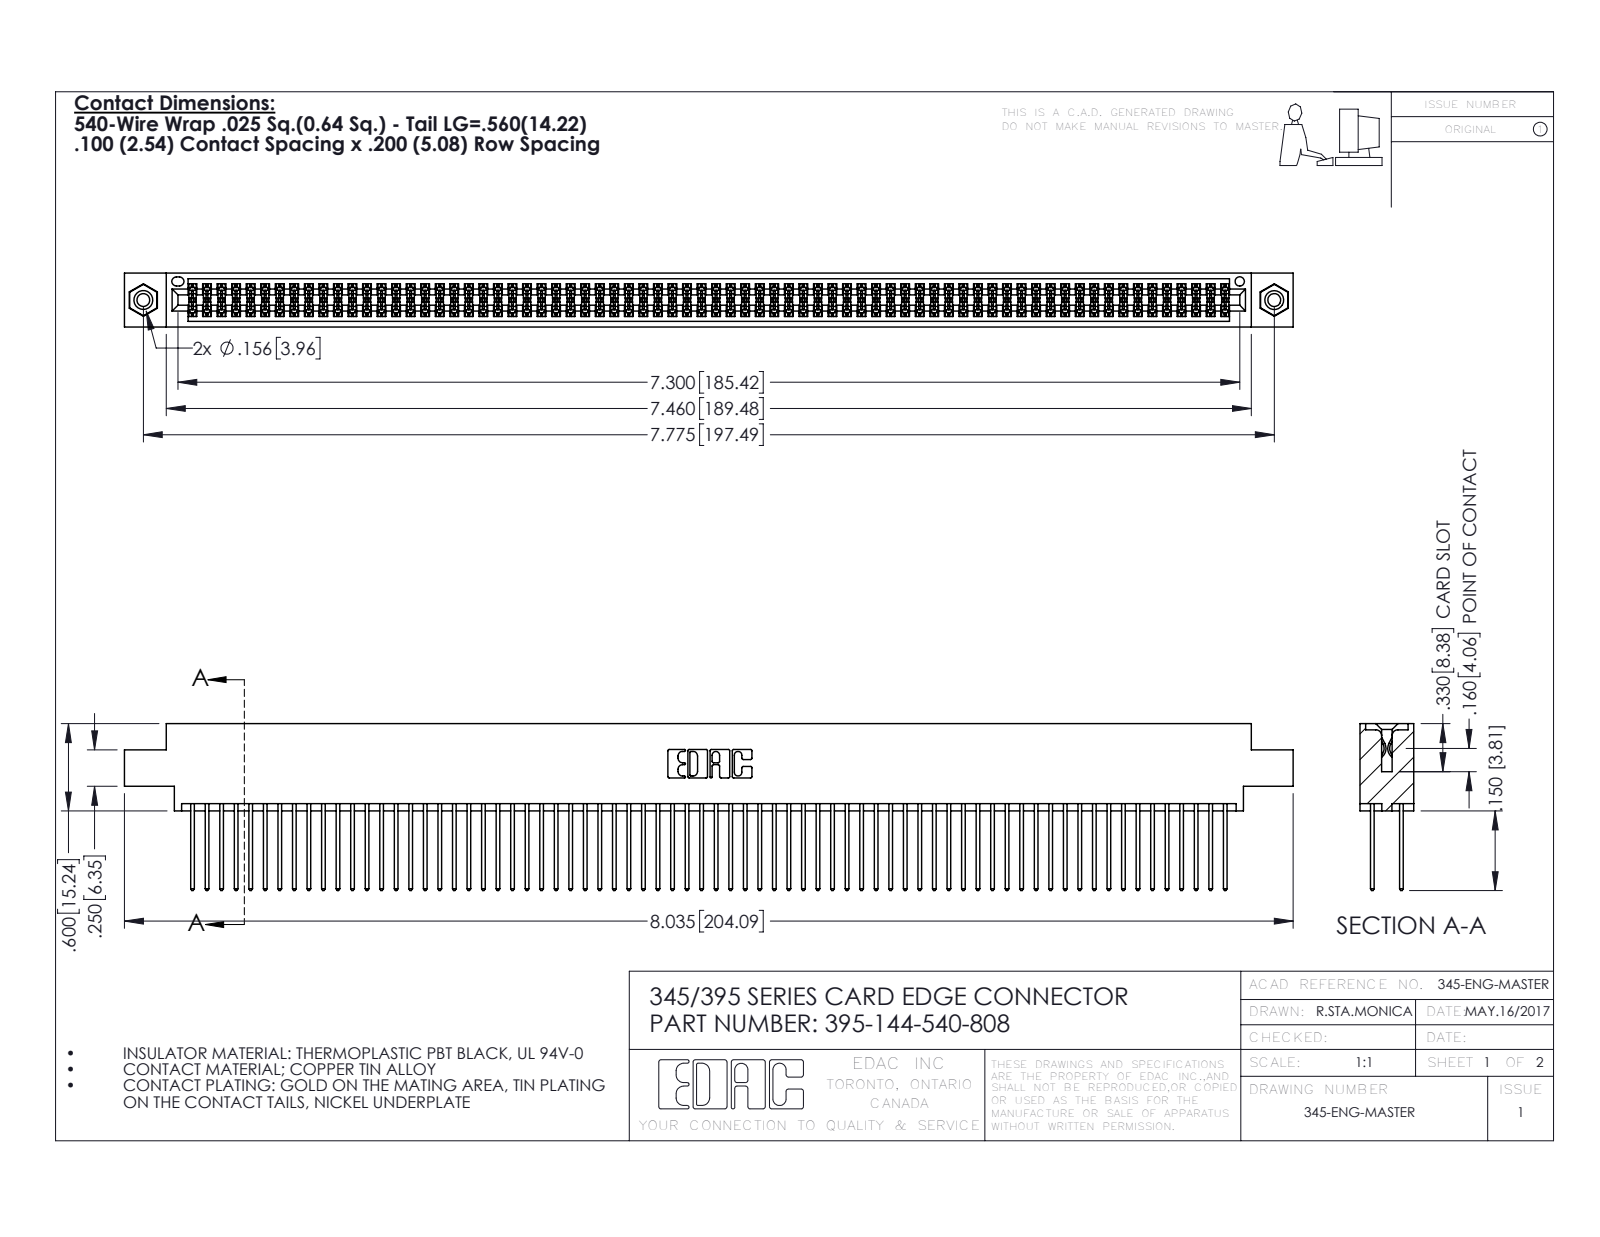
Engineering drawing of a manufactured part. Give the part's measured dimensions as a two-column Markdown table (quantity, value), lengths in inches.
| quantity | value |
| --- | --- |
| part name | 395-144-540-808; 345 Part_0.170 Offset - 0.156 Dia-TI; 345-250-001_345-250-003-102; 345-292-001_345-293-140 |
| STEP written by | SolidWorks 2016 (CONFIG_CONTROL_DESIGN) |
| units | inches |
| bodies | 147 solids, 7390 faces (4868 planar, 2506 cylindrical, 16 other) |
| overall size | 8.035 × 1.147 × 0.37 |
| volume | 1.253 in³ |
| surface area | 52.11 in² |
| round holes (diameter × count) | 0.089 × 2, 0.125 × 2, 0.156 × 2, 0.064 × 1 |
| round bosses / shafts (diameter × count) | 0.155 × 2 |
| partial cylindrical surfaces (radius × count) | 0.006 × 216, 0.01 × 144, 0.01 × 22, 0.007 × 6, 0.031 × 6, 0.026 × 3, 0.014 × 2, 0.019 × 2 |
| main face-to-face distances | 0.072, 0.298, 0.2, 0.098, 0.272, 0.025, 0.37, 0.225, 0.175, 0.149 |
| hole center spacings | 0.27, 7.539, 7.775 |
